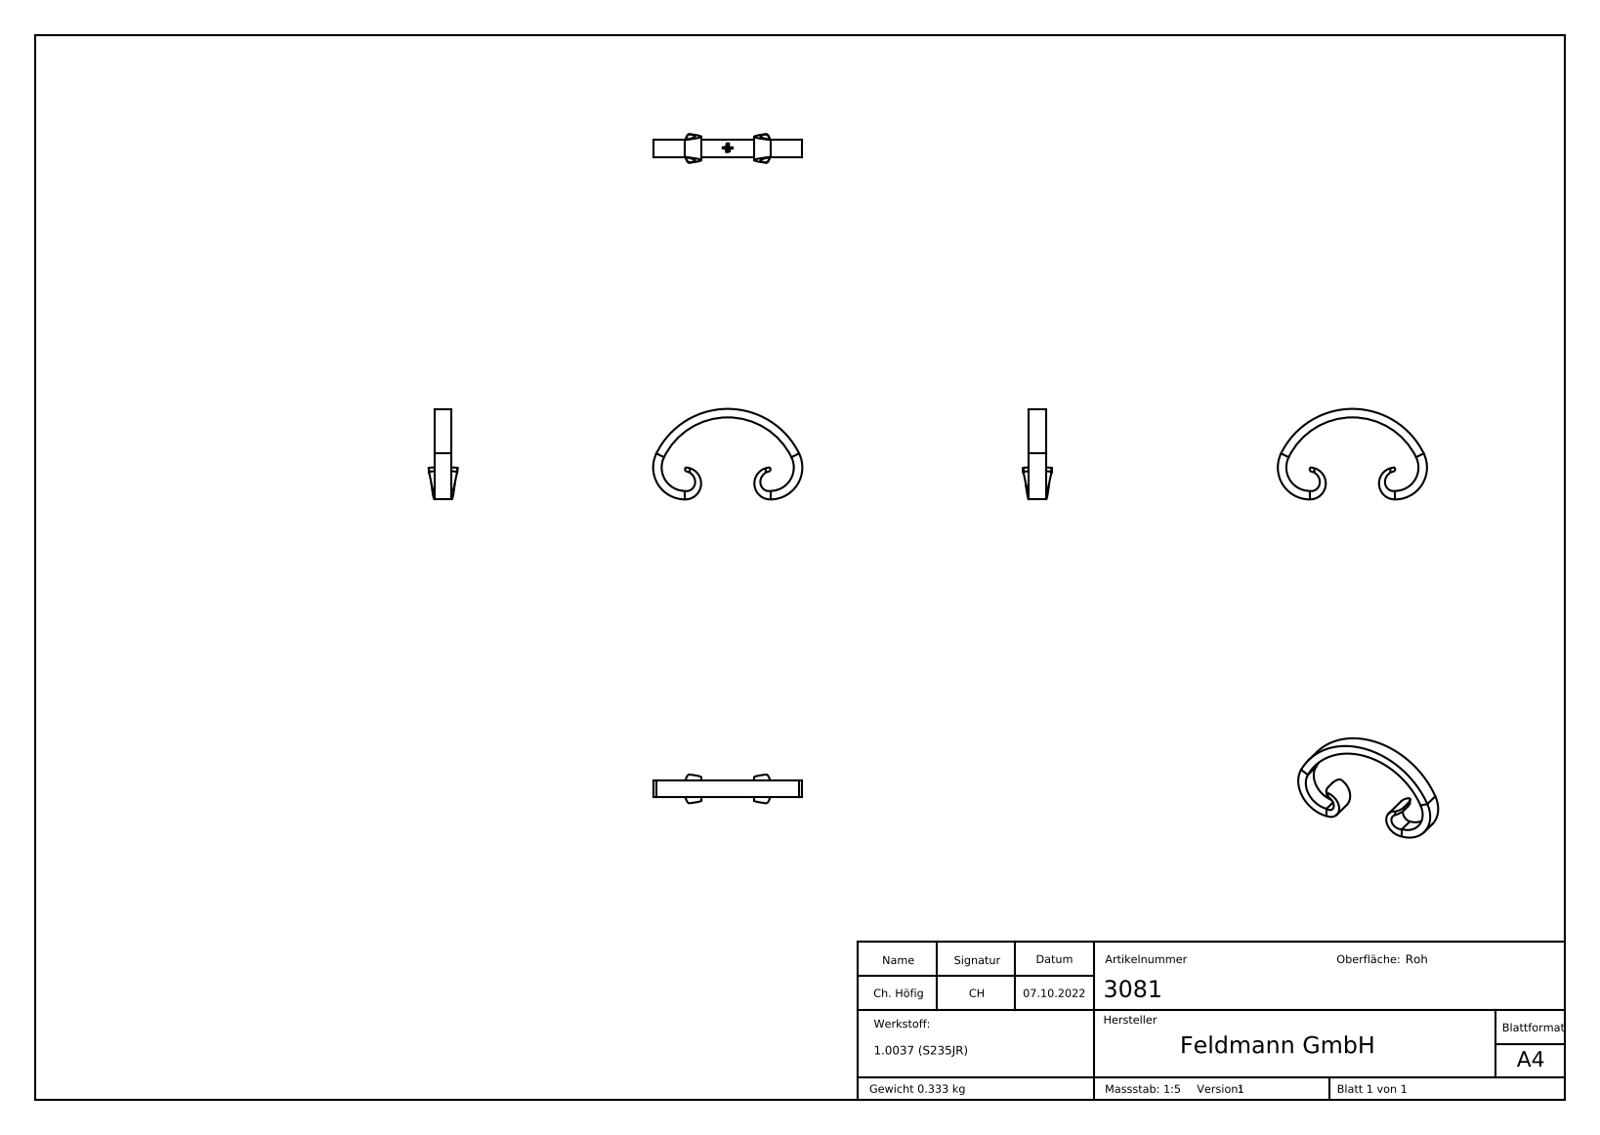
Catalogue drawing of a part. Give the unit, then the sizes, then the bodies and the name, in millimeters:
Units: millimetres
Overall size (bounding box): 140 × 85 × 26.94
Partial cylindrical surfaces — rounded edges, fillets, slot ends (radius × count): R22 ×2, R30 ×2, R66.5 ×1, R66.6 ×1, R74.5 ×1
Main face-to-face distances: 16, 80, 3.15, 2.21, 0.39, 2.84, 0.34, 8, 38.99, 41.01
Volume: 42 688 mm³ · Surface area: 16 962 mm²
Bodies: 1 solid, 238 faces (93 planar, 25 cylindrical, 120 other)
Part name (STEP PRODUCT): 3081
STEP written by: SolidWorks 2018 (CONFIG_CONTROL_DESIGN)
